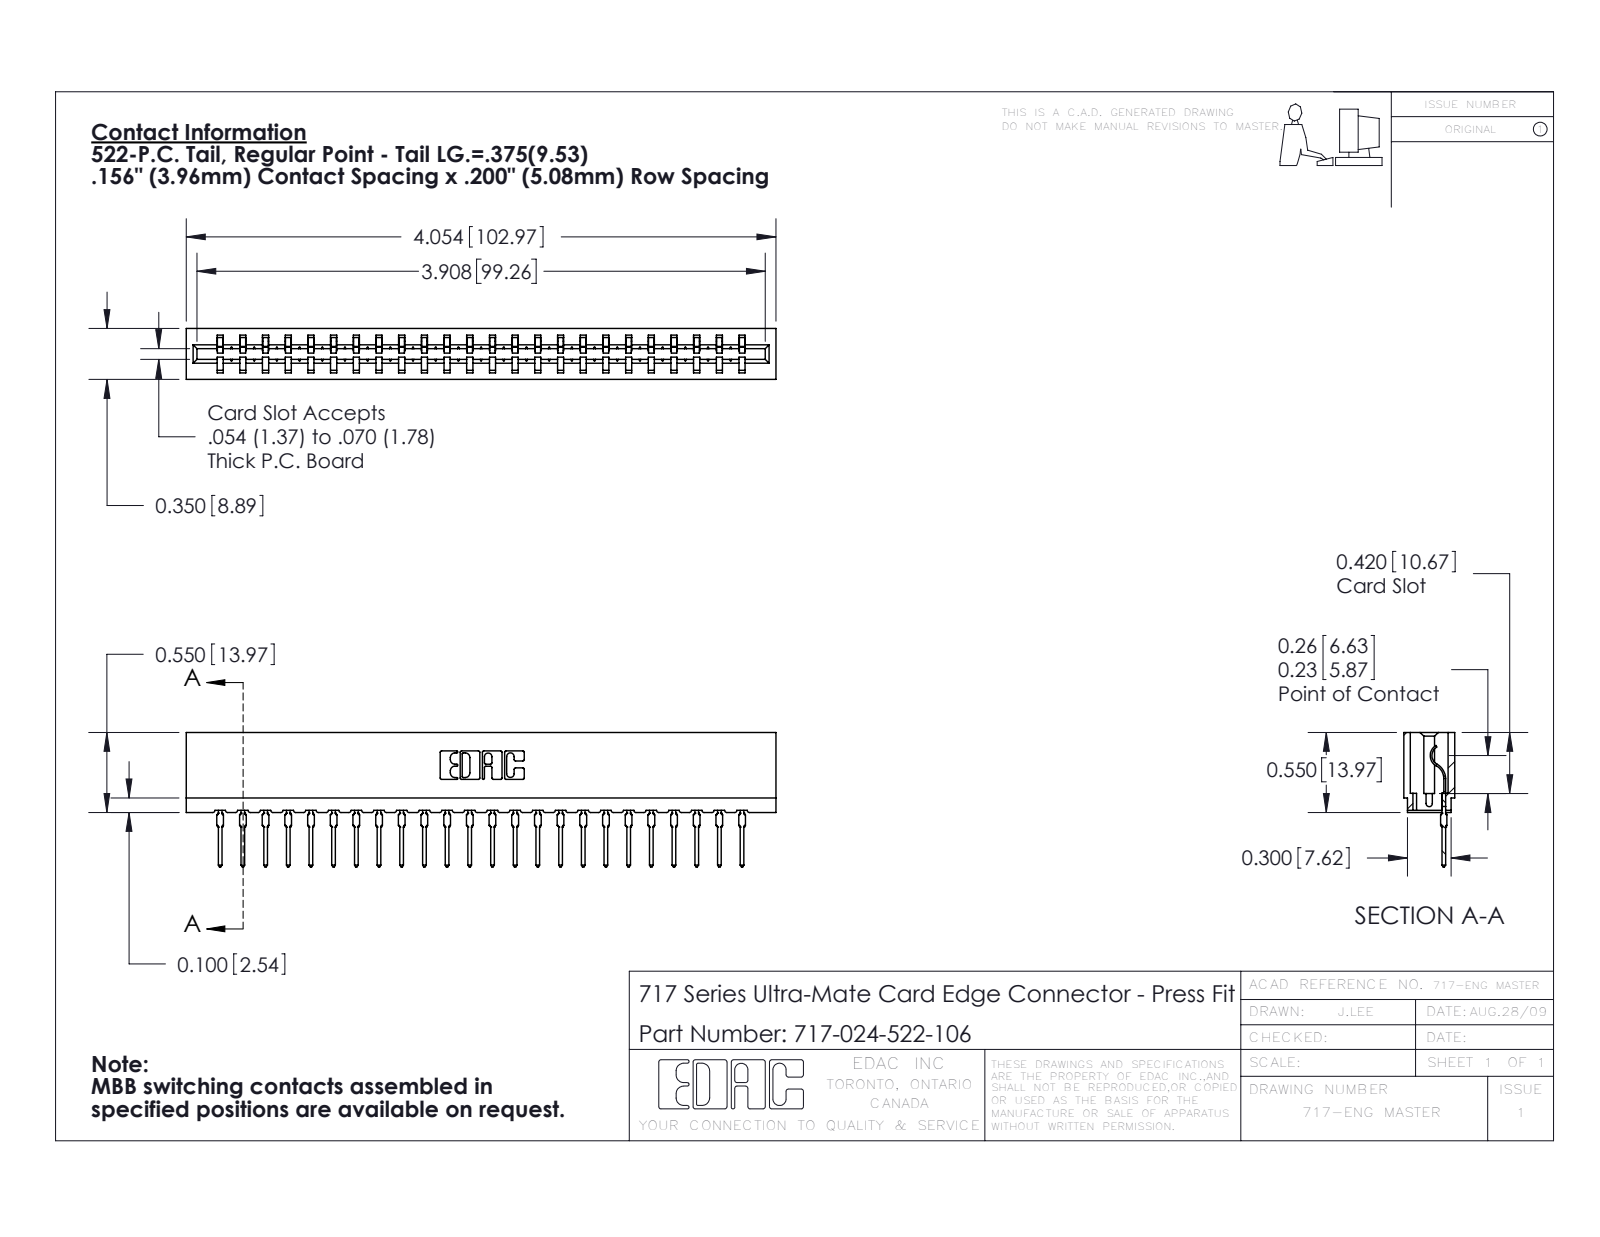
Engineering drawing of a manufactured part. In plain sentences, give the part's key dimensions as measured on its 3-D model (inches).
The part is named "717 Part_Insulator Option - 06; 717-024-522-106; 745-292-001_522". Its 3-D file was written by "SolidWorks 2016 (CONFIG_CONTROL_DESIGN)". It is 25 solids with 2806 faces: 1686 planar, 496 cylindrical and 624 other. Overall it measures 4.054 by 0.924 by 0.35 inches. Its volume is 0.536 cubic inches and its surface area 18.91 square inches. Partial cylindrical surfaces (rounded edges, fillets, slot ends): 48 of radius 0.015, 48 of radius 0.021, 22 of radius 0.01, 6 of radius 0.007, 6 of radius 0.031, 4 of radius 0.005, 4 of radius 0.011, 3 of radius 0.026. The main face-to-face distances are 0.212, 0.138, 0.35, 0.156, 0.074, 0.624, 0.468, 0.045, 0.305, 0.093.
